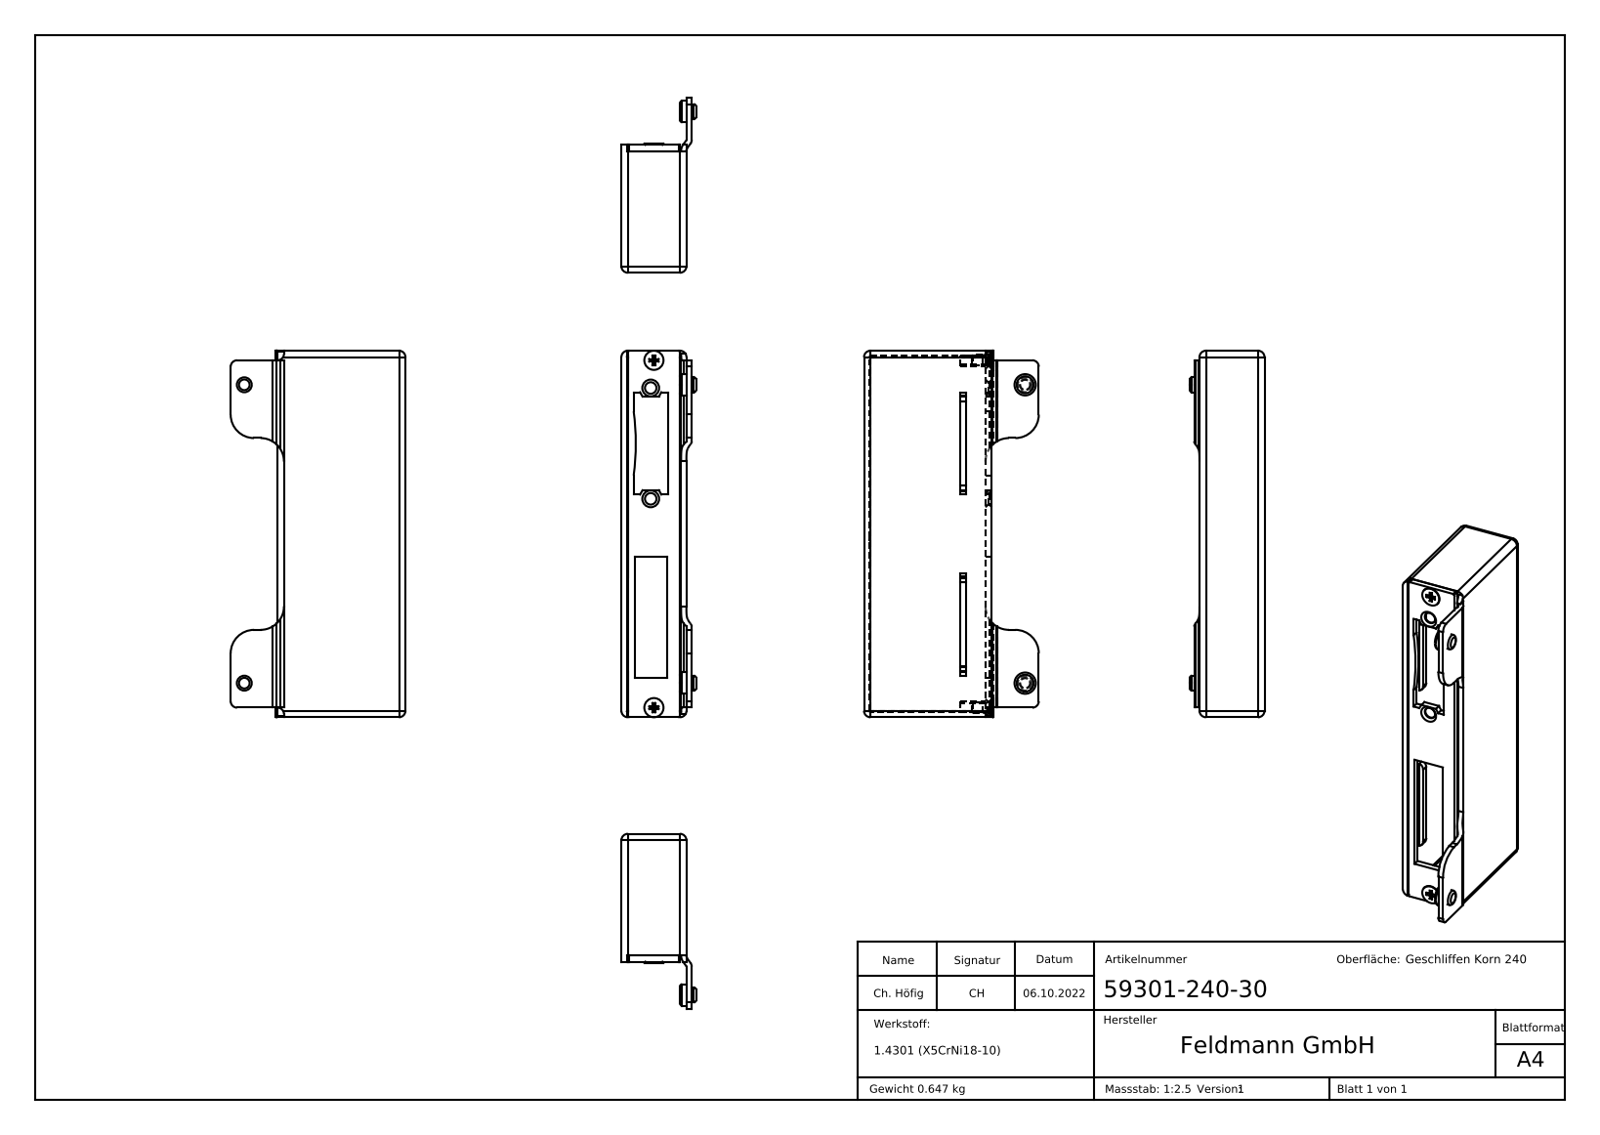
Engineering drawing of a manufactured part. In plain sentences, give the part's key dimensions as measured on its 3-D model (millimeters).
The part is named "59301-240-30; 59300-240-XX Teil1_59301-240-30 Teil1; 59300-240-XX Teil3_59305-240-30-SB; DIN 965_DIN 965 M5x10 (+1 more)". Its 3-D file was written by "SolidWorks 2018 (CONFIG_CONTROL_DESIGN)". It is 6 solids with 718 faces: 371 planar, 69 cylindrical and 278 other. Overall it measures 172 by 82 by 35 millimeters. Its volume is 82 490 cubic millimeters and its surface area 68 582 square millimeters. Round holes: 2 of diameter 4.2, 2 of diameter 4.8, 2 of diameter 5.4, 2 of diameter 5.5. Round bosses or shafts: 4 of diameter 5, 2 of diameter 10, 2 of diameter 9, 2 of diameter 7, 2 of diameter 4.6. Partial cylindrical surfaces (rounded edges, fillets, slot ends): 26 of radius 3, 13 of radius 0.5, 4 of radius 11, 1 of radius 5.5, 1 of radius 113. The main face-to-face distances are 2.5, 28, 30.5, 25.5, 3, 57, 54.5, 60, 57.5, 169.5. The hole center spacings are 13.09, 52, 65.02, 98.01, 140, 150.01, 163.
